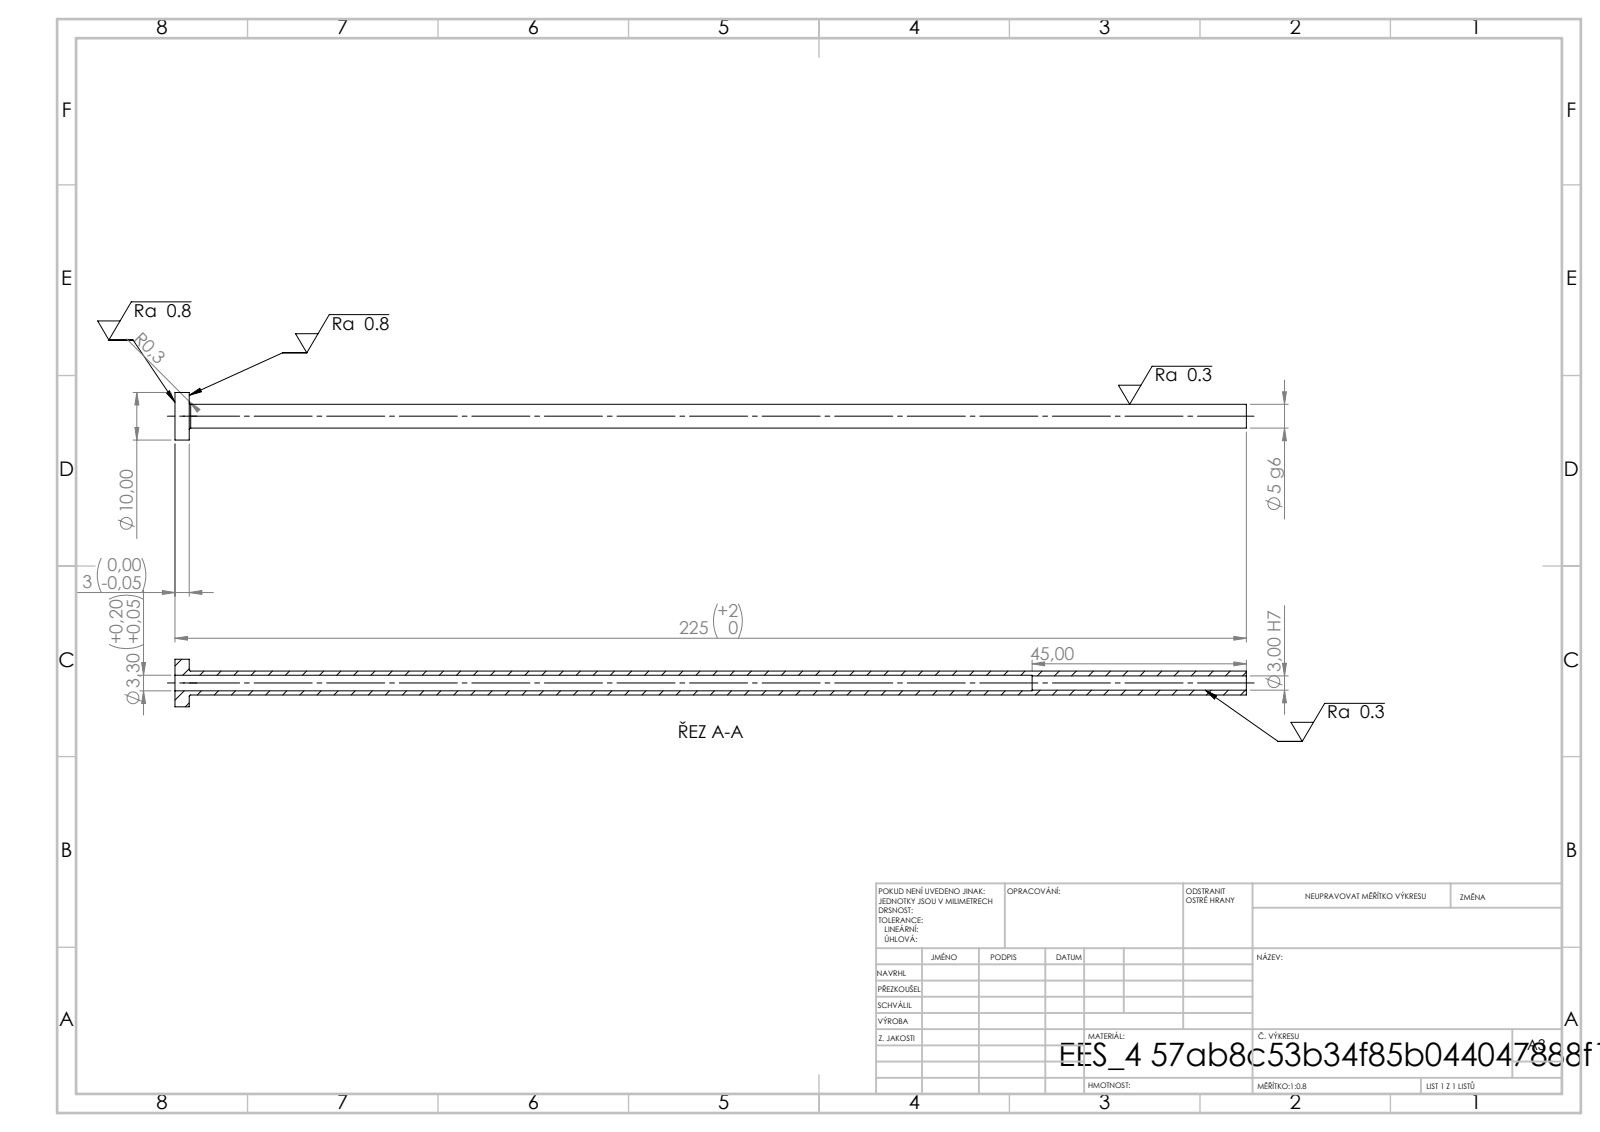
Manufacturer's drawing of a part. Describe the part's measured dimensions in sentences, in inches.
Its 3-D file was written by "SolidWorks 2019 (CONFIG_CONTROL_DESIGN)". It is 1 solid with 14 faces: 4 planar, 8 cylindrical and 2 other. Overall it measures 8.858 by 0.394 by 0.394 inches. Its volume is 0.167 cubic inches and its surface area 9.32 square inches. Round holes: 1 of diameter 0.118, 1 of diameter 0.13. Round bosses or shafts: 1 of diameter 0.394, 1 of diameter 0.197. The main face-to-face distances are 0.118, 8.858, 8.74, 7.087, 6.969, 1.772.
